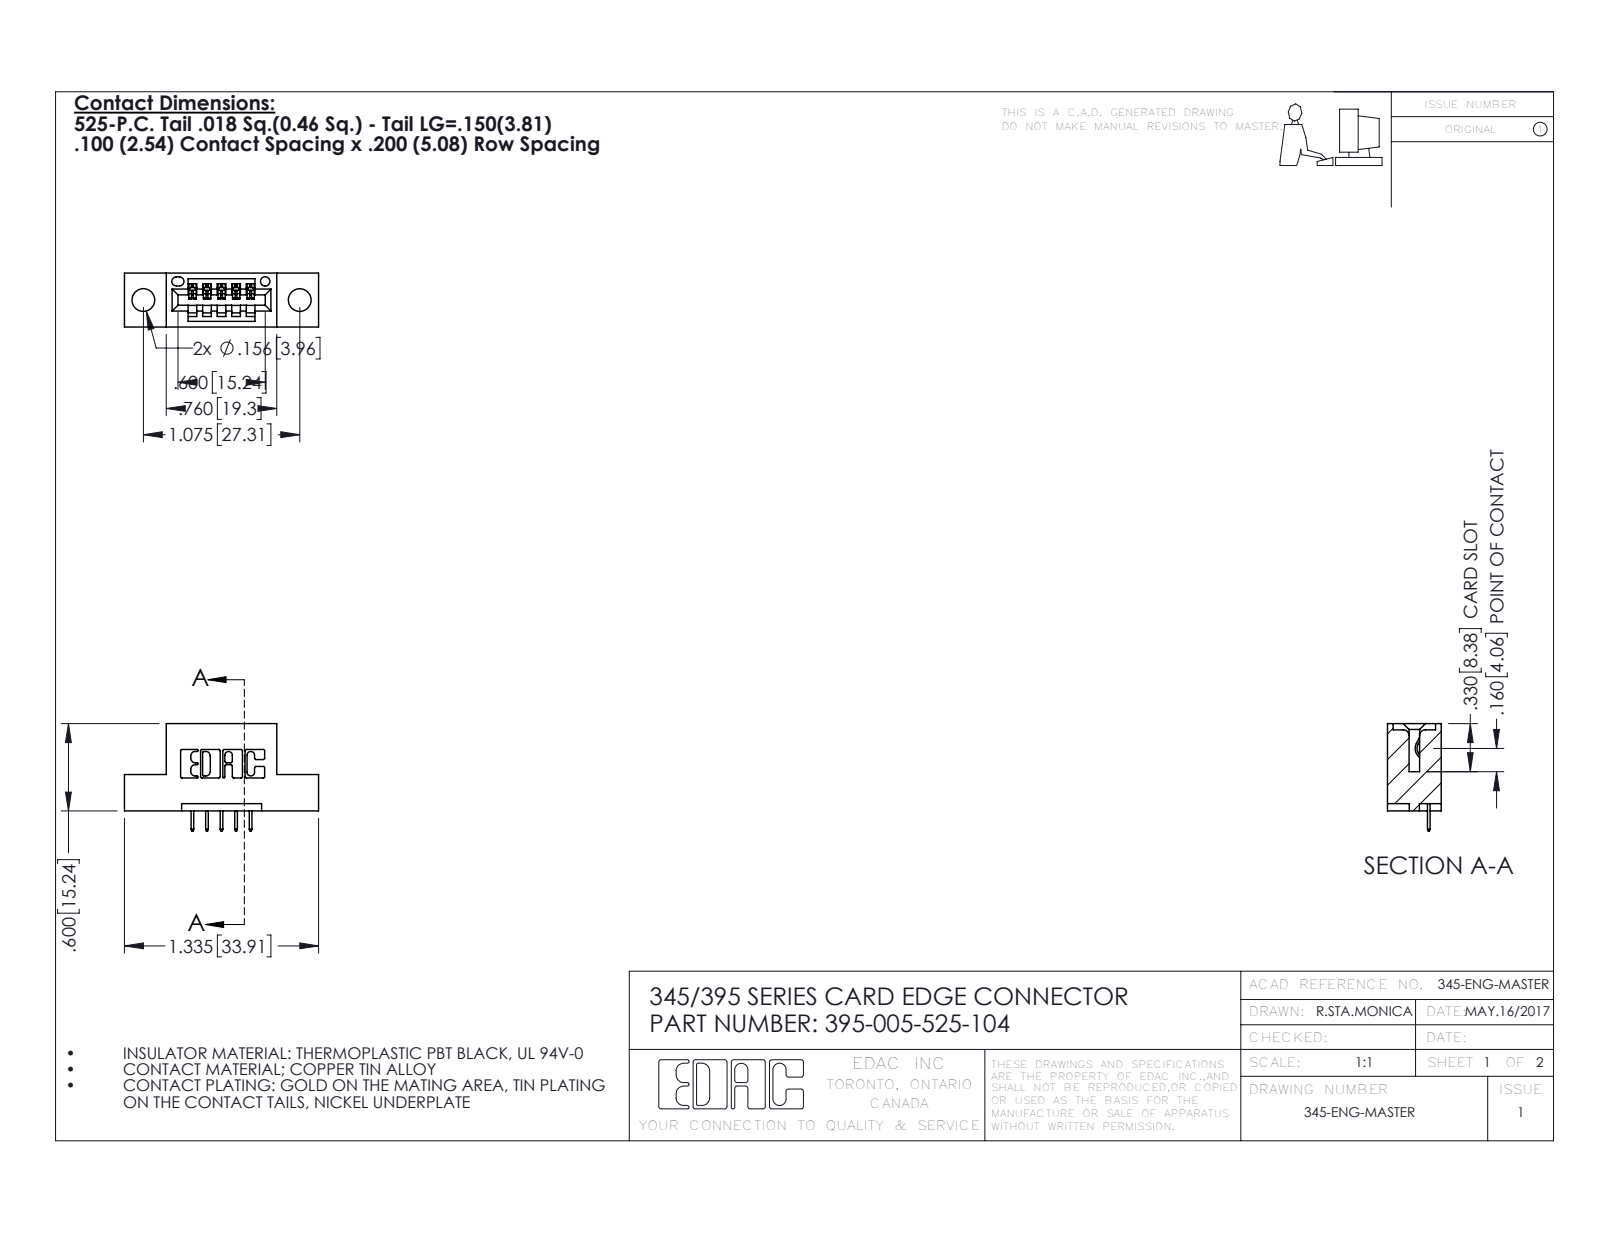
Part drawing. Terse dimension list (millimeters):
name: 395-005-525-104; 345-292-001_345-293-125; 345 Part_Flush Mounting Lugs - 0.156 Dia-TH
written by: SolidWorks 2020 (CONFIG_CONTROL_DESIGN)
unit: mm
bodies: 6 solids, 436 faces (310 planar, 126 cylindrical, 0 other)
size: 33.9 × 18.7 × 9.4
volume: 2 800 mm³; area: 2 971 mm²
holes: 2× ⌀4, 1× ⌀1.6
rounds: 22× R0.3, 10× R0.2, 6× R0.2, 6× R0.8, 3× R0.7, 2× R0.8, 2× R1, 1× R0.4
face distances: 5.1, 9.4, 2.5, 7.6, 1.8, 6.4, 1.5, 0.6, 14, 8.9
hole spacings: 6.9, 21.5, 27.3
